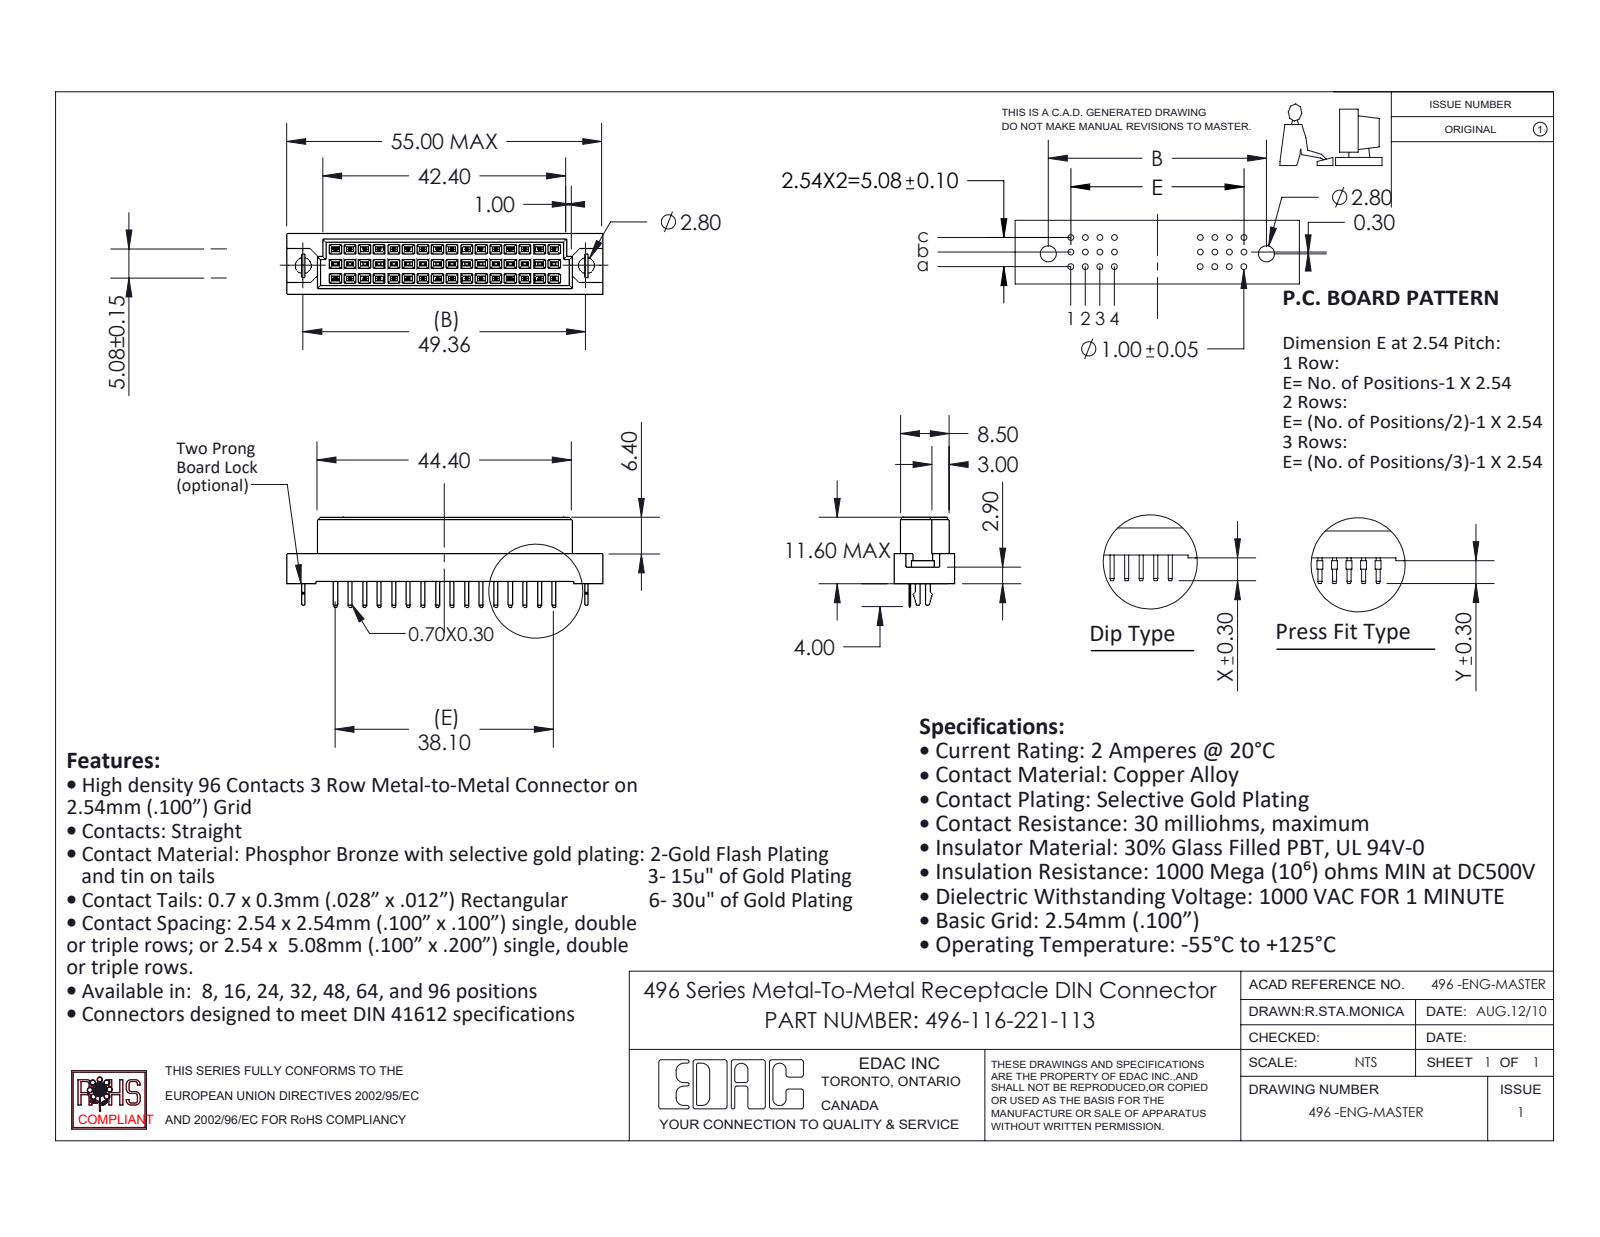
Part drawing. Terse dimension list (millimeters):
name: 496-116-221-113; 496 Bore-lock; 496 Part_48; 496-290_21
written by: SolidWorks 2020 (CONFIG_CONTROL_DESIGN)
unit: mm
bodies: 19 solids, 862 faces (856 planar, 6 cylindrical, 0 other)
size: 55 × 15.6 × 10.6
volume: 4 640 mm³; area: 4 601 mm²
holes: 2× ⌀2.8
rounds: 1× R0.53
face distances: 2.54, 1.05, 9.55, 5.08, 0.81, 10.6, 3.35, 1.73, 8.5, 0.56
hole spacings: 49.36
